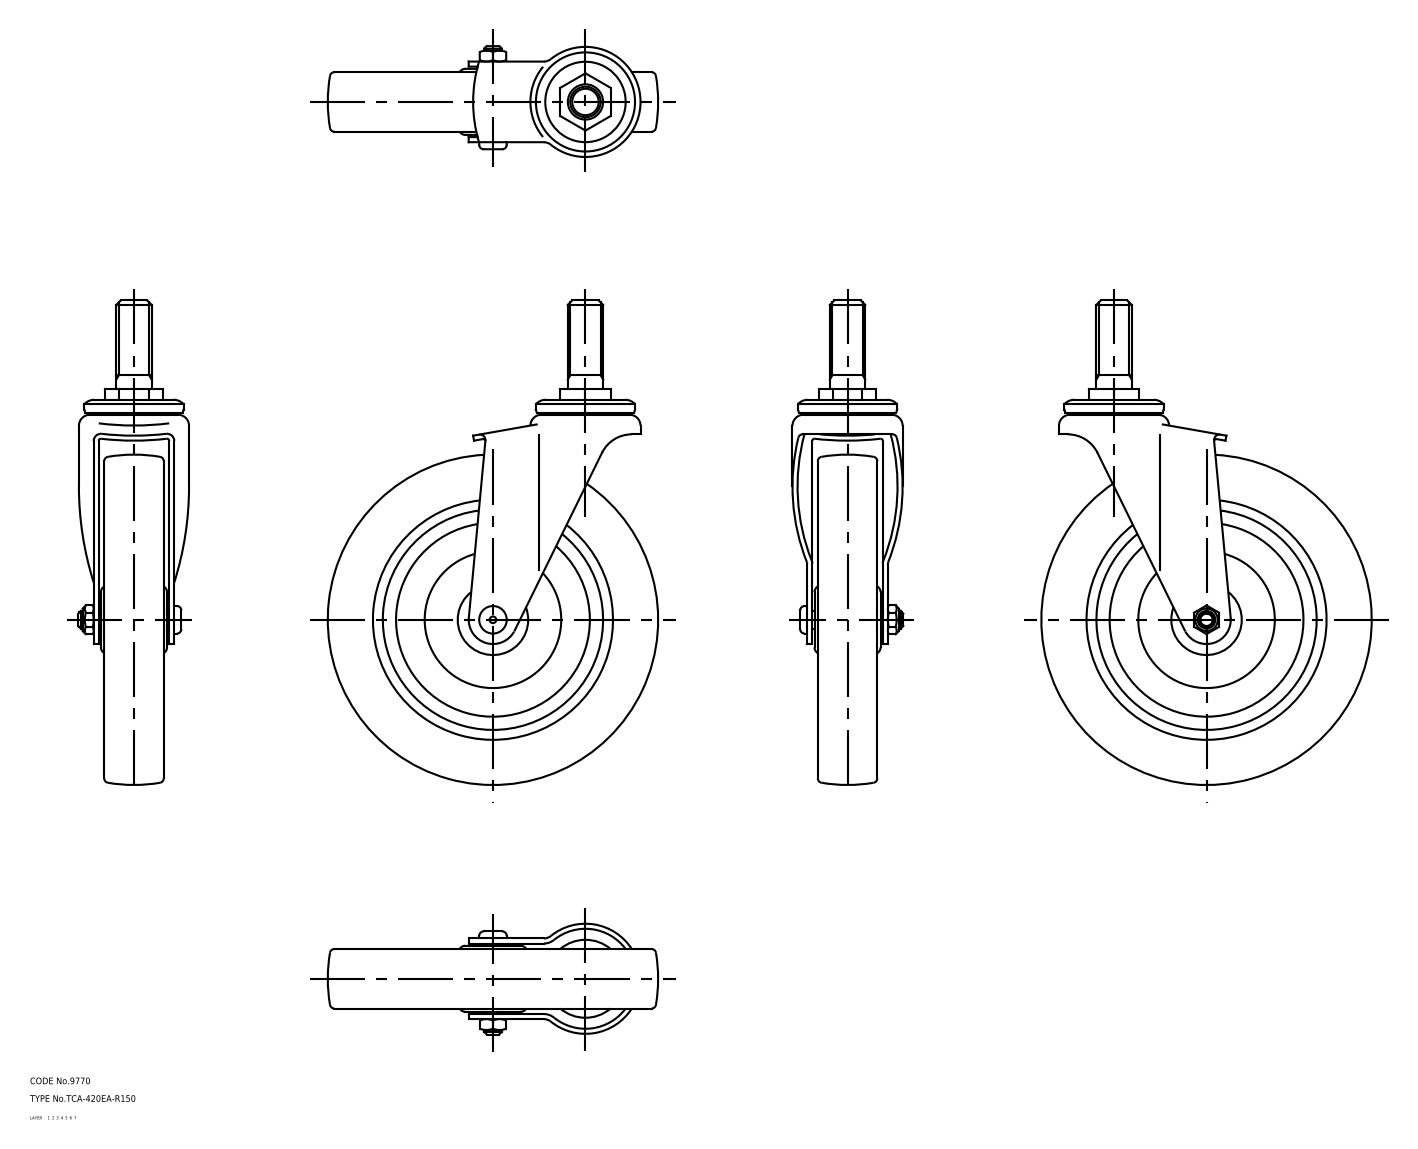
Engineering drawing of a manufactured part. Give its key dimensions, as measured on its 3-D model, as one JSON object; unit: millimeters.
{"part_name": "wheel; mounting plate; main shaft; axle (+1 more)", "step_written_by": "CADfix (AUTOMOTIVE_DESIGN)", "units": "millimeters", "bodies": {"solids": 5, "faces": 230, "planar": 0, "cylindrical": 0, "other": 230}, "overall_size": [220, 150, 50.3], "volume_mm3": 512106, "surface_area_mm2": 83777}
